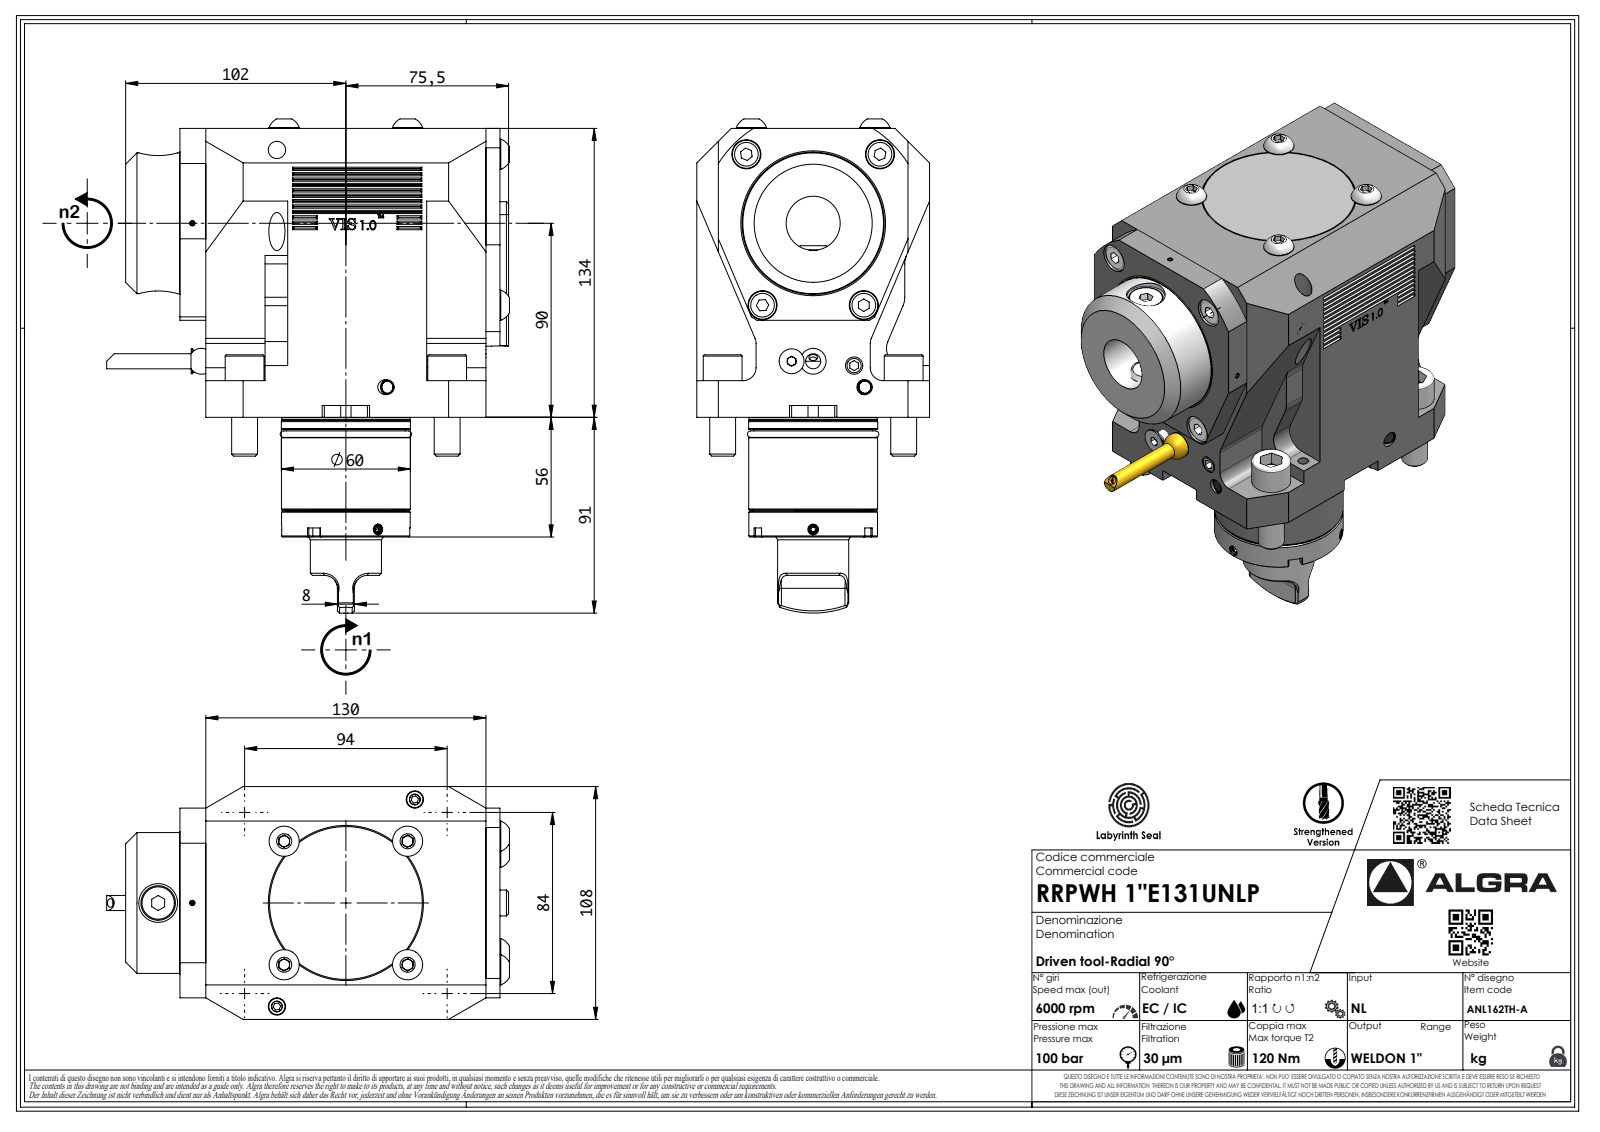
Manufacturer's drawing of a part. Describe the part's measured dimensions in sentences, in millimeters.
The part is named "RRPWH1E131UNLP". Its 3-D file was written by "SolidWorks 2023 (AUTOMOTIVE_DESIGN)". It is 1 solid with 933 faces: 648 planar, 118 cylindrical and 167 other. Overall it measures 224.8 by 186.5 by 108 millimeters. Its volume is 2 042 000 cubic millimeters and its surface area 129 943 square millimeters. Round holes: 1 of diameter 2.1, 1 of diameter 4, 1 of diameter 14, 1 of diameter 18, 1 of diameter 25.1. Round bosses or shafts: 4 of diameter 18, 4 of diameter 12, 1 of diameter 65.3, 1 of diameter 59.9, 1 of diameter 59.8, 1 of diameter 59.7, 1 of diameter 59.5, 1 of diameter 55.2. Partial cylindrical surfaces (rounded edges, fillets, slot ends): 21 of radius 0.2, 18 of radius 8, 11 of radius 6, 7 of radius 0.33, 7 of radius 0.52, 7 of radius 3.7, 4 of radius 10, 3 of radius 3. The main face-to-face distances are 134, 108, 12, 27.5, 102.5, 148.5, 6.5, 136.5, 38, 5.5.
